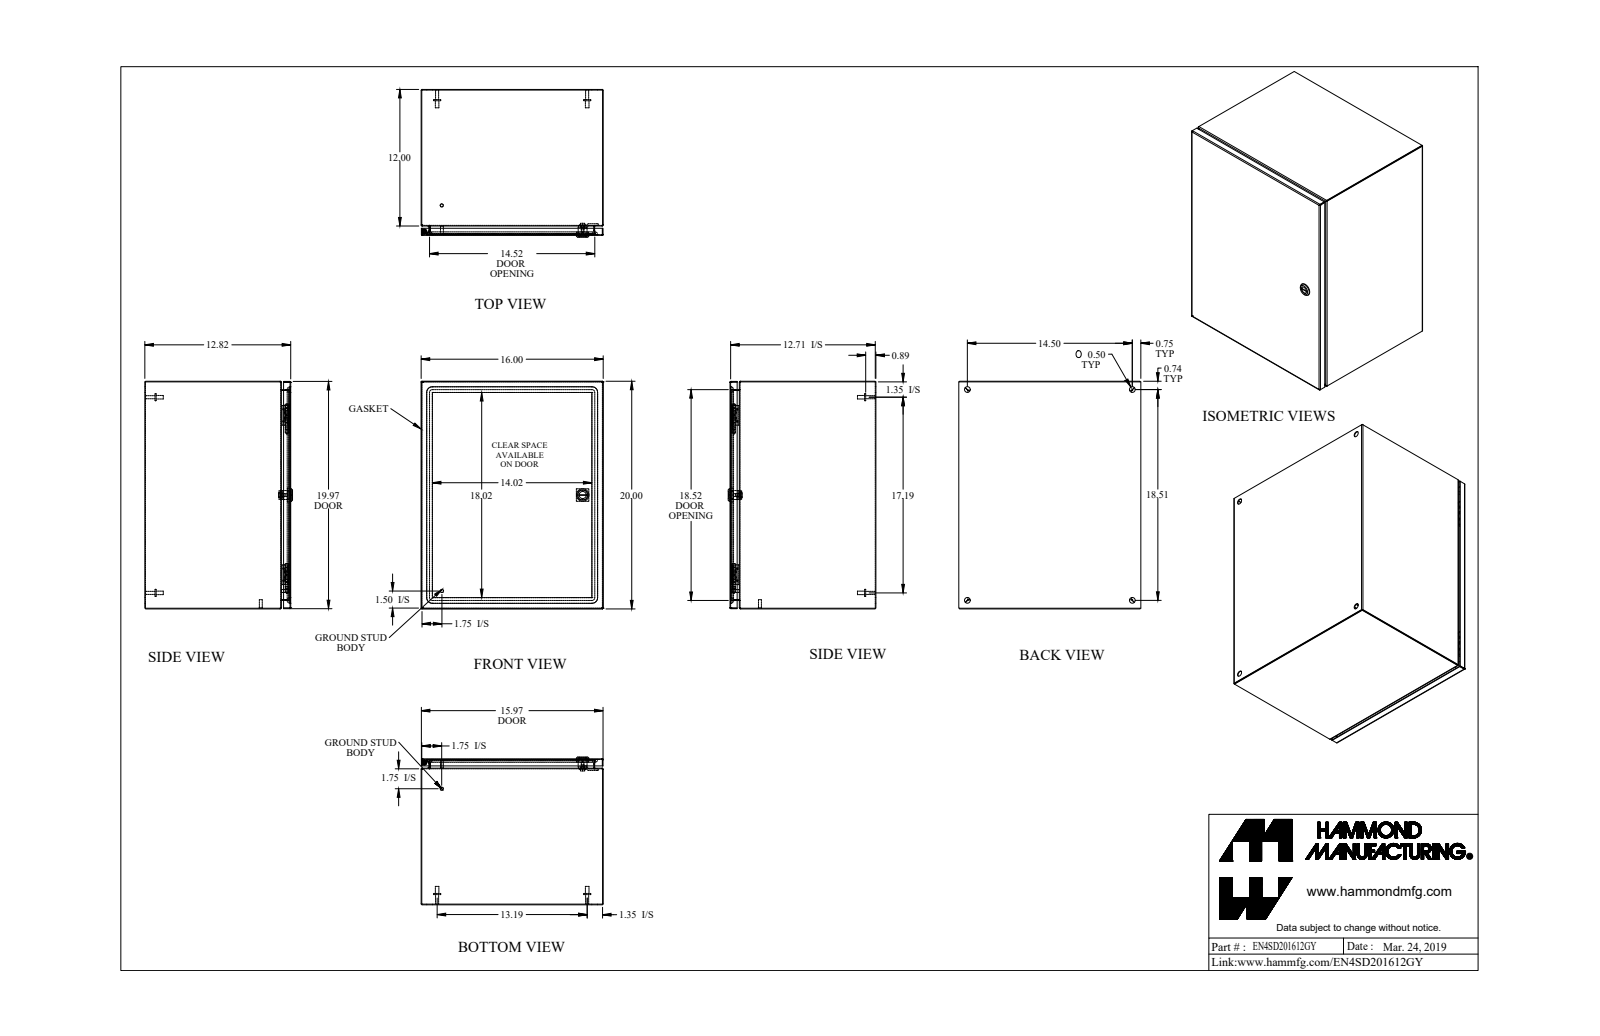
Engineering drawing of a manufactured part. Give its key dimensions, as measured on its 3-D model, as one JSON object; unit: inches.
{"part_name": "EN4SD201612GY_Default", "step_written_by": "SolidWorks 2019 (CONFIG_CONTROL_DESIGN)", "units": "inches", "bodies": {"solids": 23, "faces": 622, "planar": 293, "cylindrical": 201, "other": 128}, "overall_size": [20, 16, 12.982], "volume_in3": 100.7, "surface_area_in2": 3448, "round_holes": [[0.5, 4], [0.172, 1], [0.232, 1], [0.24, 1], [0.242, 1], [0.625, 1], [0.785, 1]], "round_bosses_or_shafts": [[0.625, 4], [0.313, 4], [0.27, 4], [0.281, 2], [0.25, 2], [1.1, 1], [0.525, 1], [0.455, 1]], "partial_cylinders_radius": [[0.029, 19], [0.086, 19], [0.188, 12], [0.006, 4], [0.062, 4], [0.25, 4], [0.499, 4], [0.125, 2]], "face_to_face_distances": [0.057, 12.765, 15.943, 19.943, 12.708, 12.822, 15.886, 16, 19.886, 20], "hole_center_spacings": [14.5, 18.514, 23.516, 9.309, 9.326, 16.317, 16.326]}
